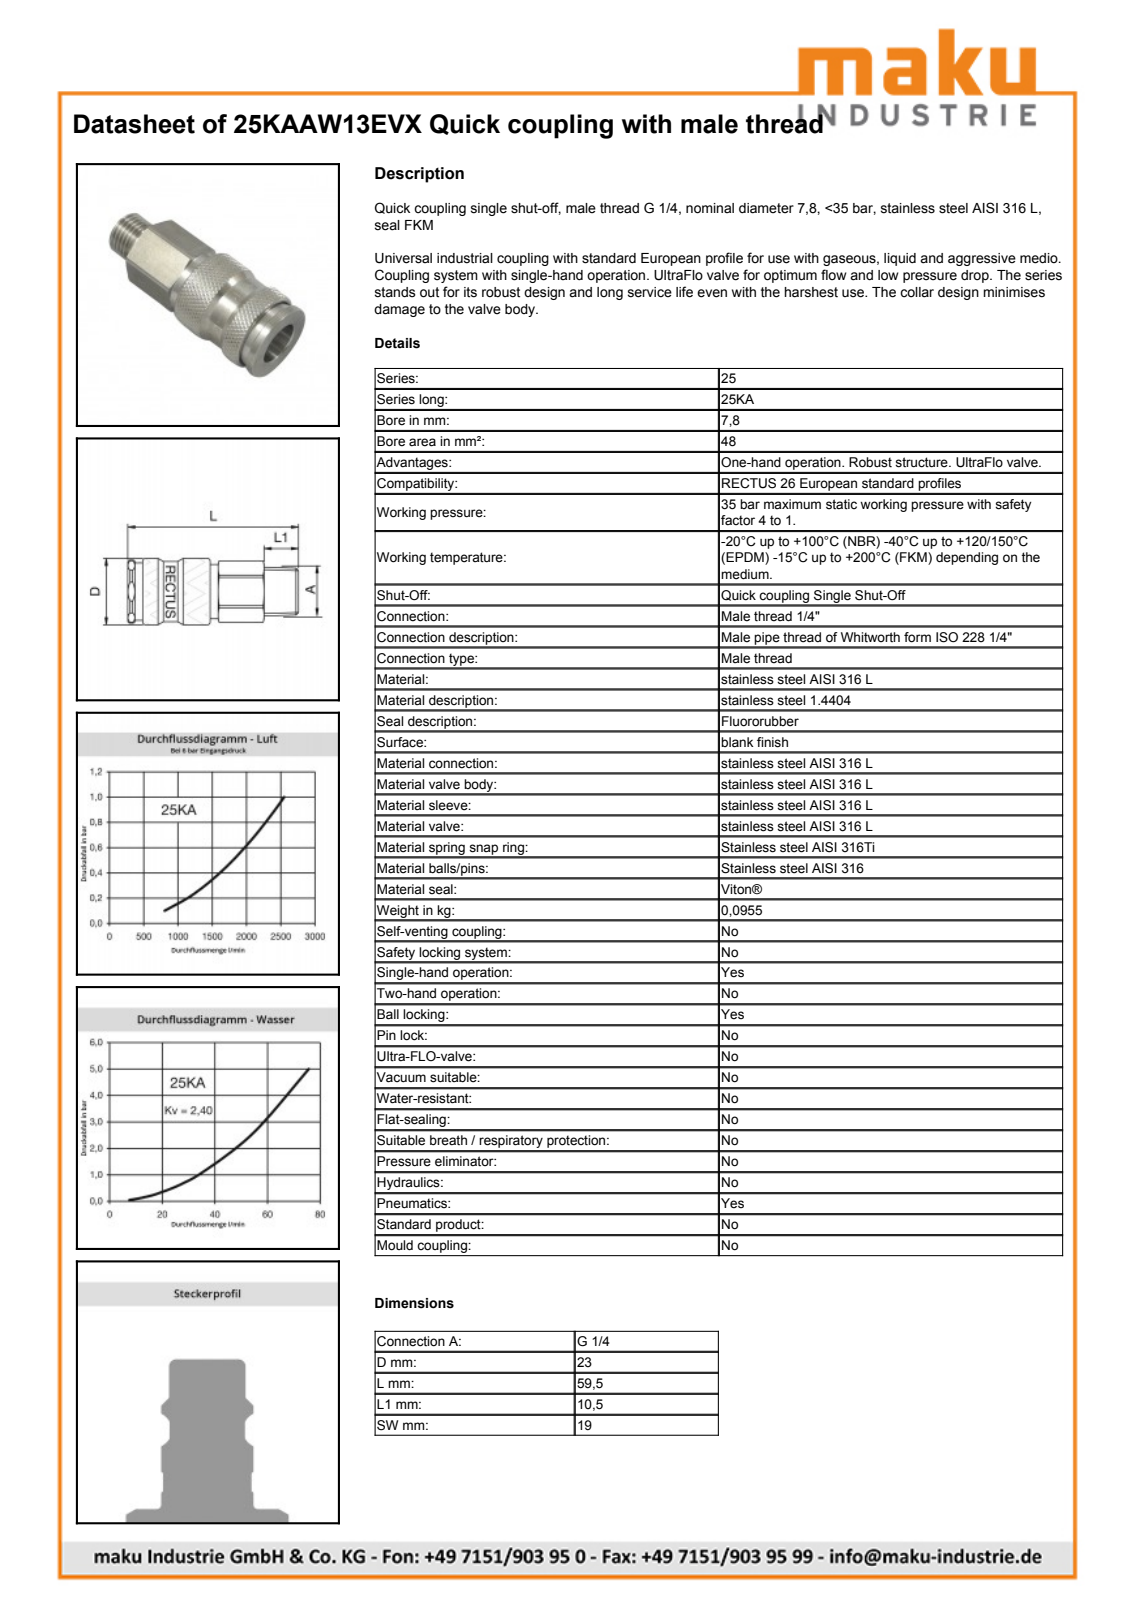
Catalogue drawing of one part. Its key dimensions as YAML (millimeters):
part_name: "D105663"
step_written_by: "Autodesk Inventor 2011 (AUTOMOTIVE_DESIGN)"
units: millimeters
bodies: {solids: 2, faces: 616, planar: 213, cylindrical: 86, other: 317}
overall_size: [59.5, 23.15, 23.15]
volume: 17299
surface_area: 8064
round_holes:
  - {diameter: 15.1, count: 1}
  - {diameter: 16, count: 1}
  - {diameter: 17.25, count: 1}
  - {diameter: 19.35, count: 1}
  - {diameter: 20.05, count: 1}
round_bosses_or_shafts:
  - {diameter: 23.15, count: 1}
  - {diameter: 21, count: 1}
  - {diameter: 20, count: 1}
  - {diameter: 18.95, count: 1}
  - {diameter: 17, count: 1}
  - {diameter: 15.3, count: 1}
  - {diameter: 15, count: 1}
  - {diameter: 14.81, count: 1}
partial_cylinders:
  - {radius: 10.4, count: 1}
  - {radius: 10.7, count: 1}
  - {radius: 11, count: 1}
face_to_face_distances: [19, 19.02, 24.5, 59.5, 10.5, 49, 35, 5.25, 19.25, 28.75]
